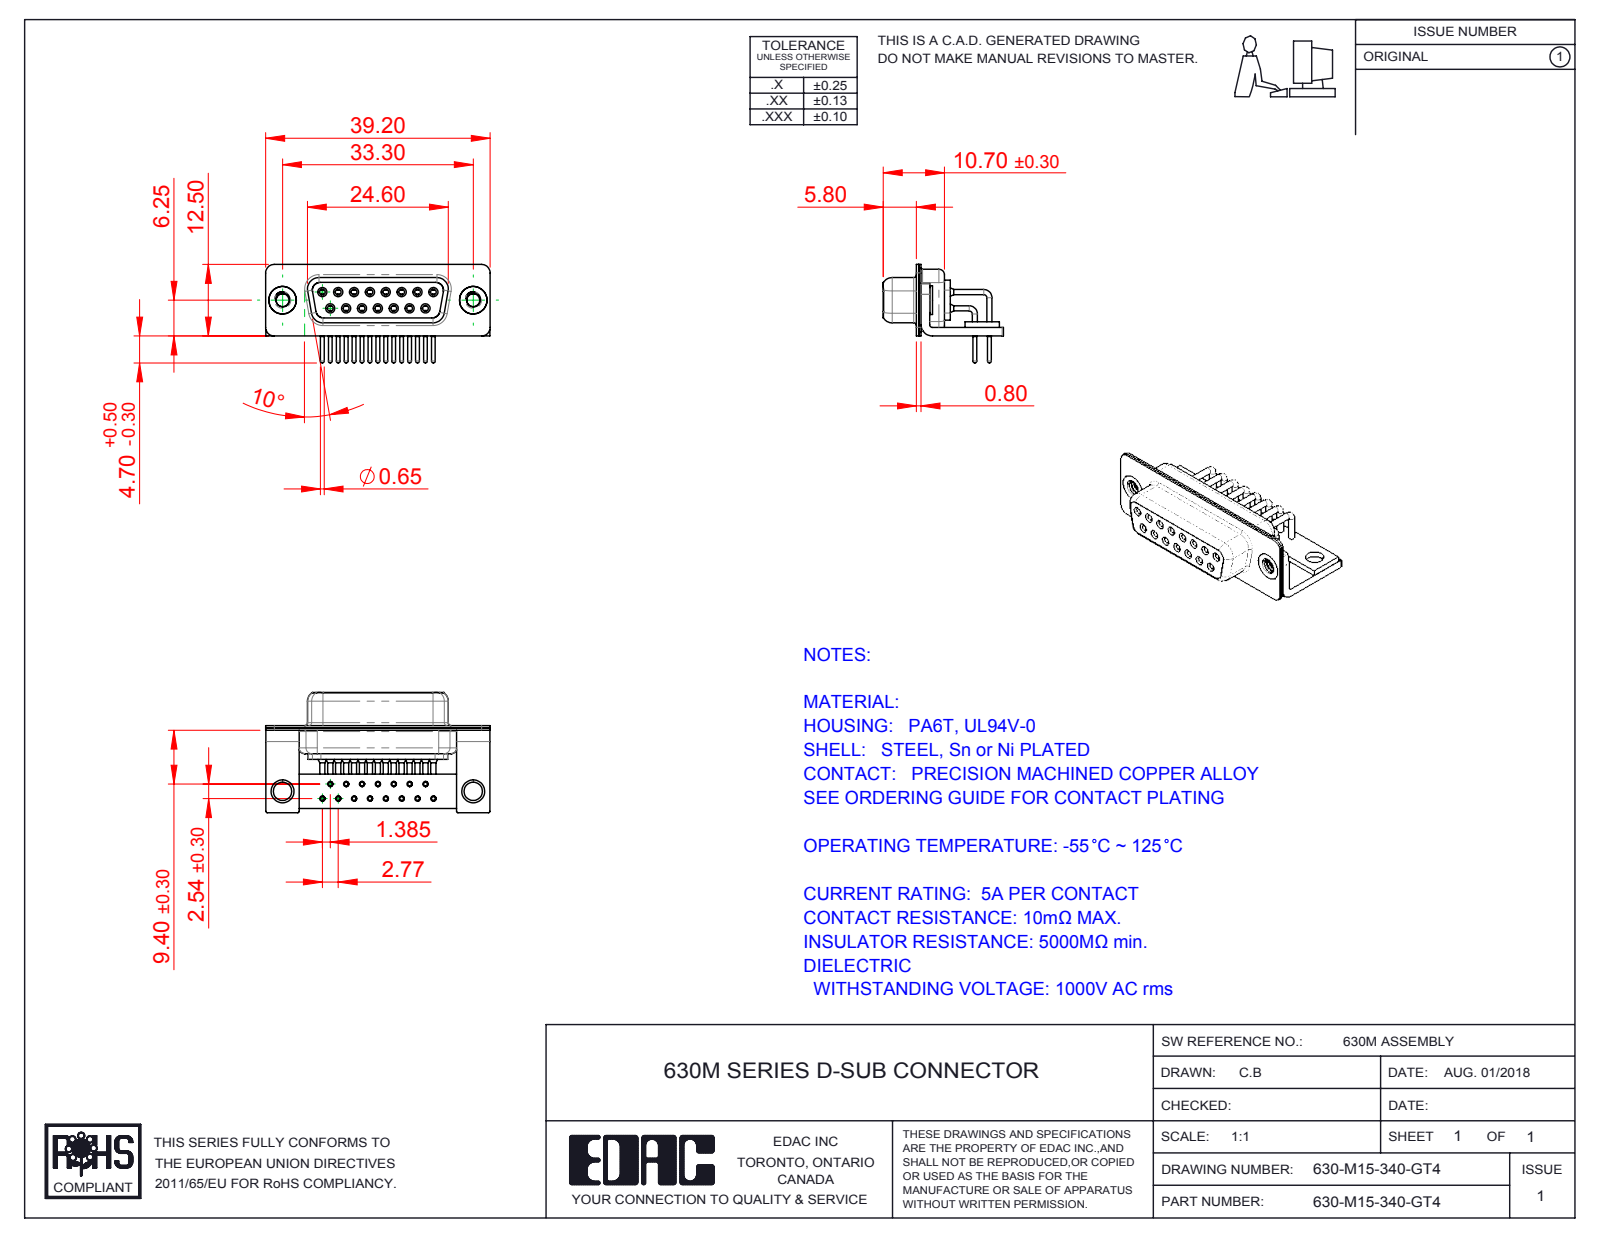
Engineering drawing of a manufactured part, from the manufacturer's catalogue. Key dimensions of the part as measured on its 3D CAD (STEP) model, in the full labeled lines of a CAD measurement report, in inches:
Part name (STEP PRODUCT): 630M 4-40 Threaded Rivet_Stabilizer; 630-M15-340-GT4; 630M Shell Rear_15 Contacts; 630M Housing_15 Contacts (+5 more)
STEP written by: SolidWorks 2016 (CONFIG_CONTROL_DESIGN)
Units: inches
Bodies: 23 solids, 1154 faces (318 planar, 534 cylindrical, 302 other)
Overall size (bounding box): 1.543 × 0.827 × 0.677
Volume: 0.186 in³ · Surface area: 11.96 in²
Round holes (diameter × count): ⌀0.035 ×15, ⌀0.039 ×15, ⌀0.043 ×15, ⌀0.067 ×15, ⌀0.071 ×15, ⌀0.079 ×15, ⌀0.089 ×2, ⌀0.126 ×2, ⌀0.157 ×2, ⌀0.189 ×2
Round bosses / shafts (diameter × count): ⌀0.035 ×27, ⌀0.063 ×15, ⌀0.059 ×15, ⌀0.026 ×15, ⌀0.197 ×2, ⌀0.193 ×2
Partial cylindrical surfaces — rounded edges, fillets, slot ends (radius × count): R0.01 ×16, R0.059 ×16, R0.079 ×13, R0.053 ×8, R0.063 ×8, R0.02 ×5, R0.024 ×4, R0.026 ×4
Main face-to-face distances: 0.016, 0.031, 0.091, 0.368, 0.075, 0.059, 0.039, 0.057, 0.352, 0.033
Hole centre spacings: 0.109, 0.218, 0.327, 0.124, 0.192, 0.436, 0.114, 0.29
